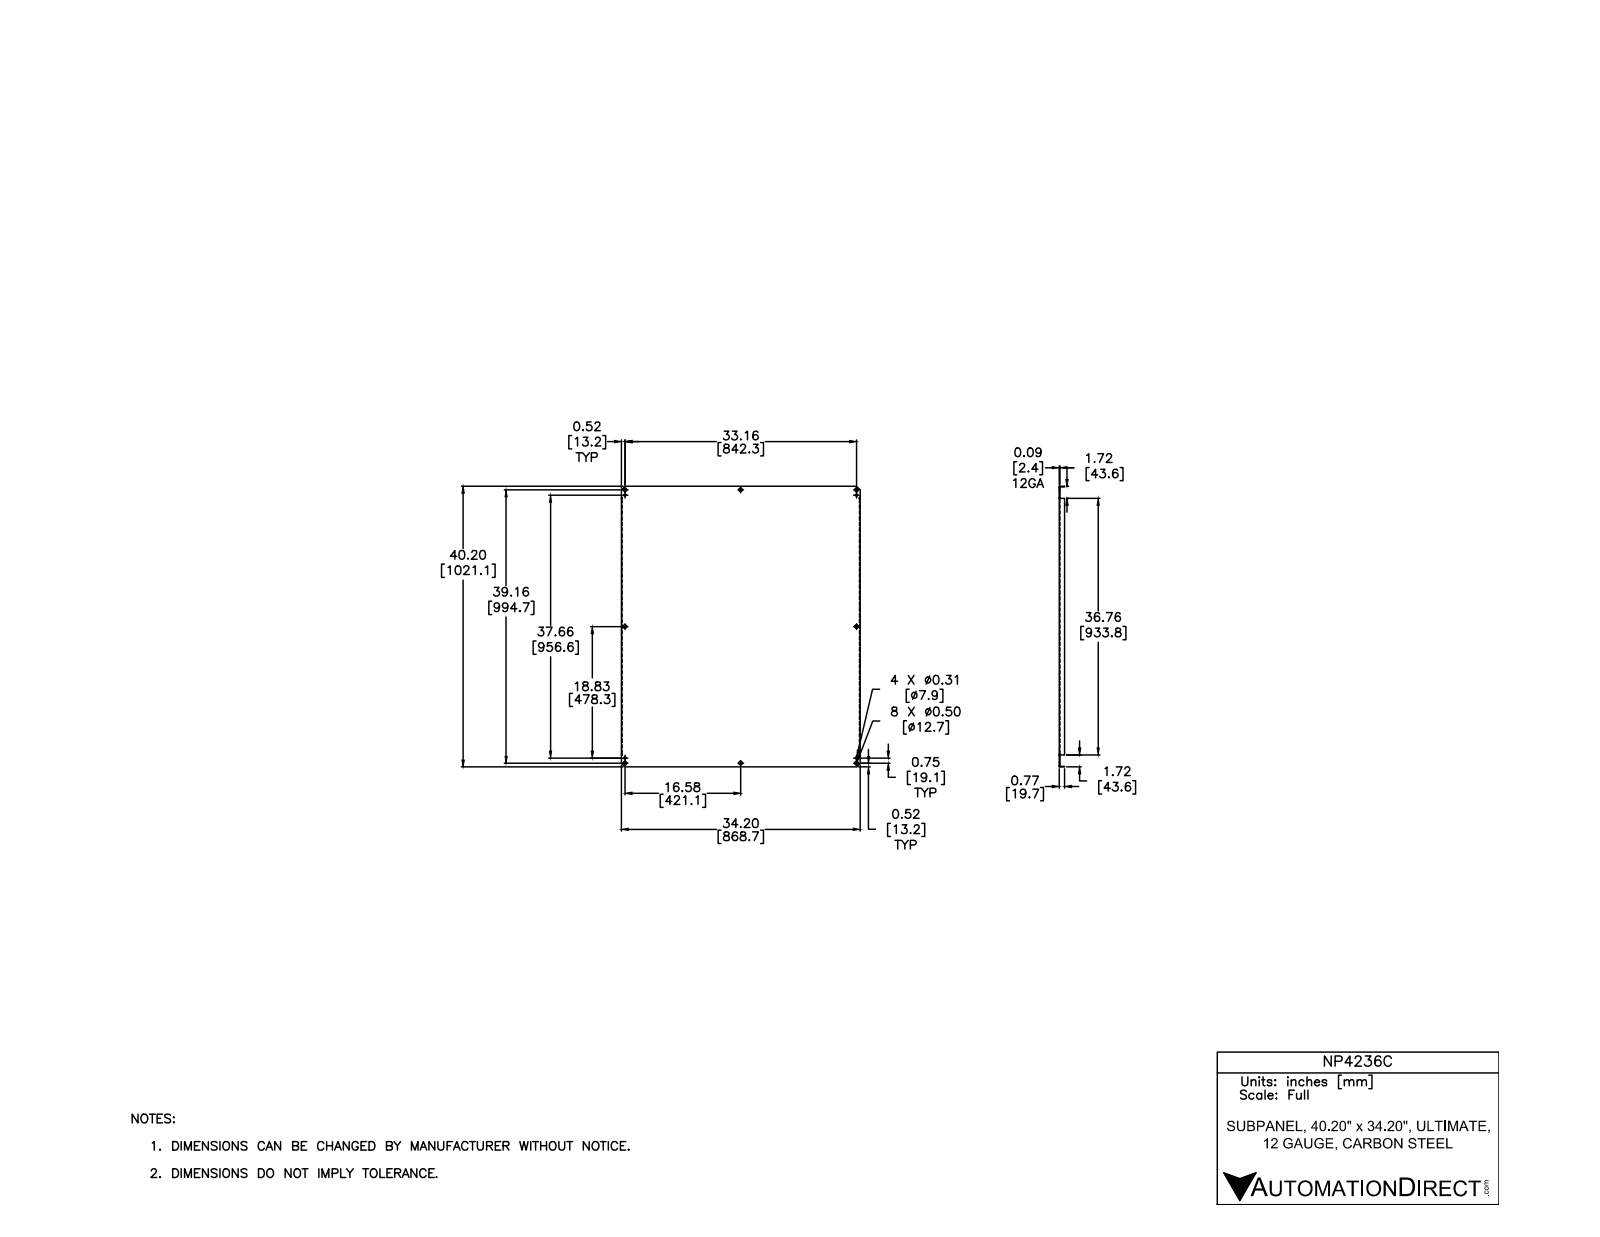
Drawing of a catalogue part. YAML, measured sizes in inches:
part_name: "NP4236C"
step_written_by: "Autodesk Inventor 2012 (AUTOMOTIVE_DESIGN)"
units: inches
bodies: {solids: 1, faces: 70, planar: 50, cylindrical: 20, other: 0}
overall_size: [40.2, 34.2, 0.774]
volume: 136.9
surface_area: 2937
round_holes:
  - {diameter: 0.5, count: 8}
  - {diameter: 0.313, count: 4}
partial_cylinders:
  - {radius: 0.016, count: 4}
  - {radius: 0.109, count: 4}
face_to_face_distances: [0.094, 34.106, 40.106, 34.2, 34.013, 40.2, 40.013, 0.68, 0.774, 1.718]
hole_center_spacings: [33.16, 0.75, 16.58, 16.597, 18.83, 19.58, 25.657, 33.169]
